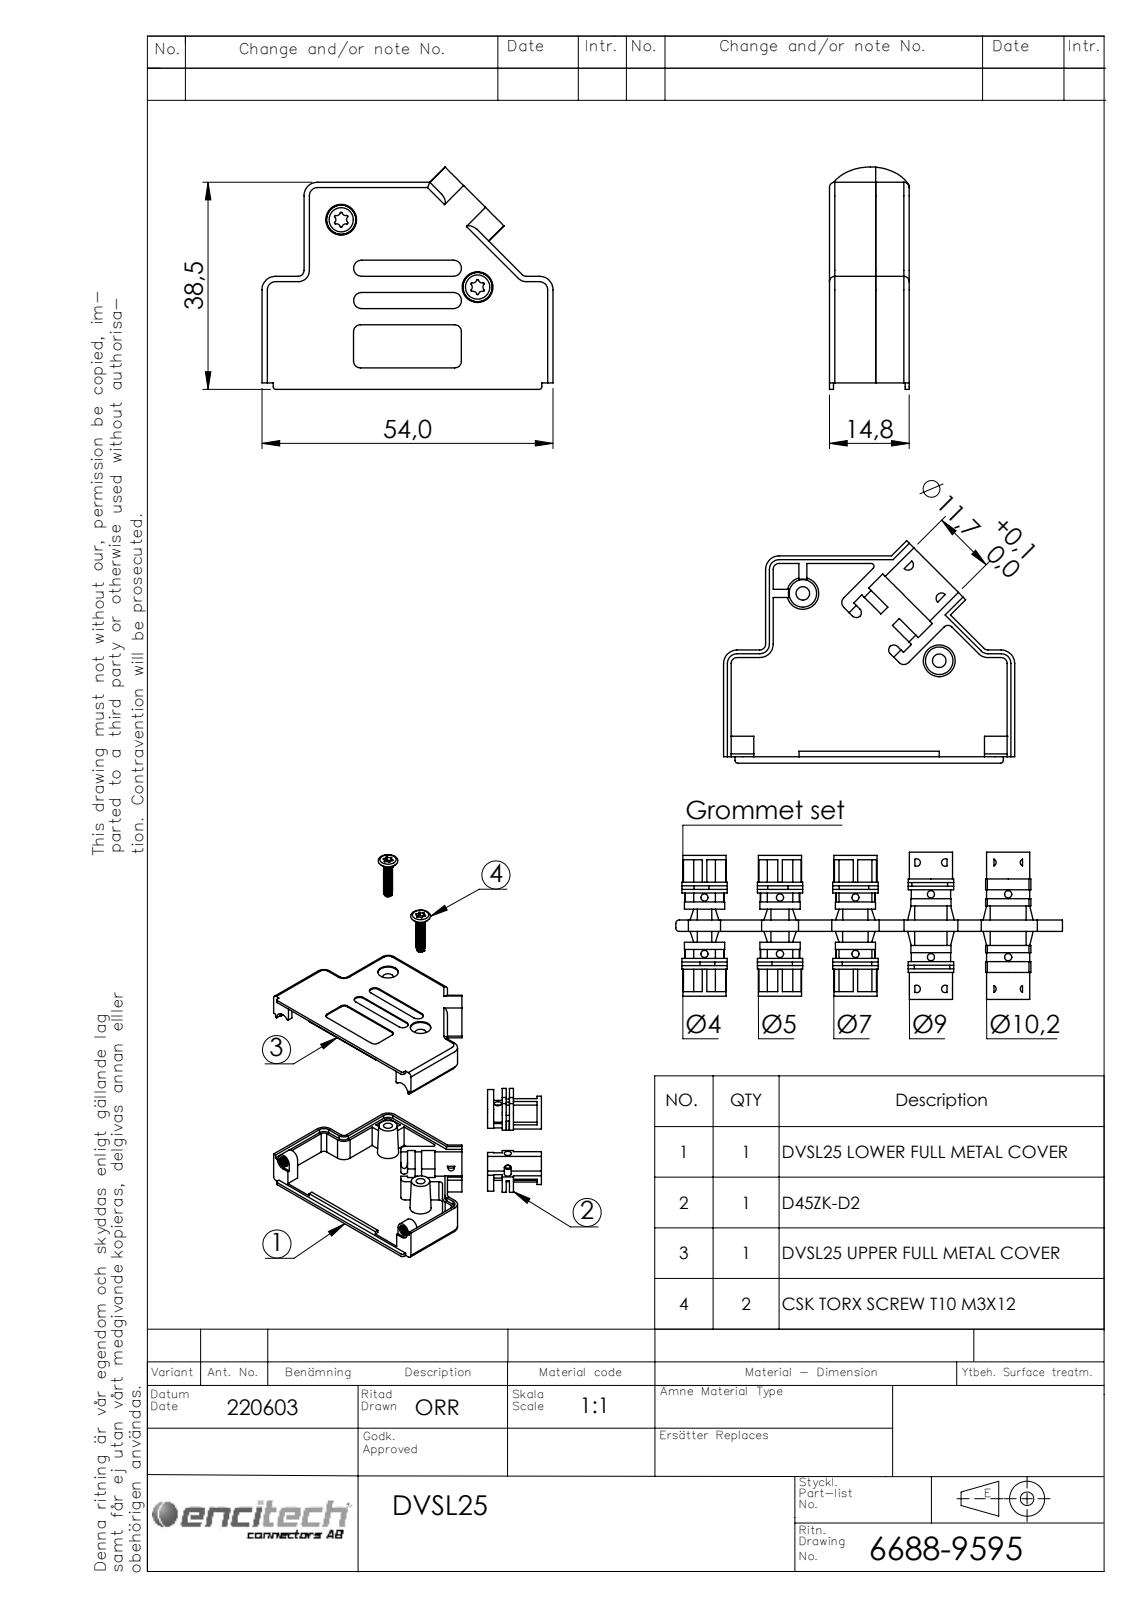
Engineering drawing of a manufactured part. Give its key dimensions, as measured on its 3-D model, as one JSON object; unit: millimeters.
{"part_name": "6688-9595; 6855-0117-12; 6805-0210-13; 6805-0210-03 (+1 more)", "step_written_by": "SolidWorks 2021 (AUTOMOTIVE_DESIGN)", "units": "millimeters", "bodies": {"solids": 6, "faces": 636, "planar": 270, "cylindrical": 302, "other": 64}, "overall_size": [54, 41.3, 14.9], "volume_mm3": 8903, "surface_area_mm2": 14012, "round_holes": [[2, 3], [2.35, 2], [3, 2], [4.7, 2], [5.7, 2], [7, 1]], "round_bosses_or_shafts": [[2.5, 2], [1.9, 2], [11.6, 1], [9.2, 1]], "partial_cylinders_radius": [[1, 23], [0.18, 12], [0.7, 12], [0.5, 10], [1.25, 6], [1.1, 5], [1.8, 5], [2.5, 5]], "face_to_face_distances": [1.35, 13.45, 14.8, 12.1, 1.4, 14.5, 1.05, 13.15, 7.2, 7.8], "hole_center_spacings": [5.71, 7.6, 10, 12.3, 14.64, 16.73, 17.42, 22.43]}
